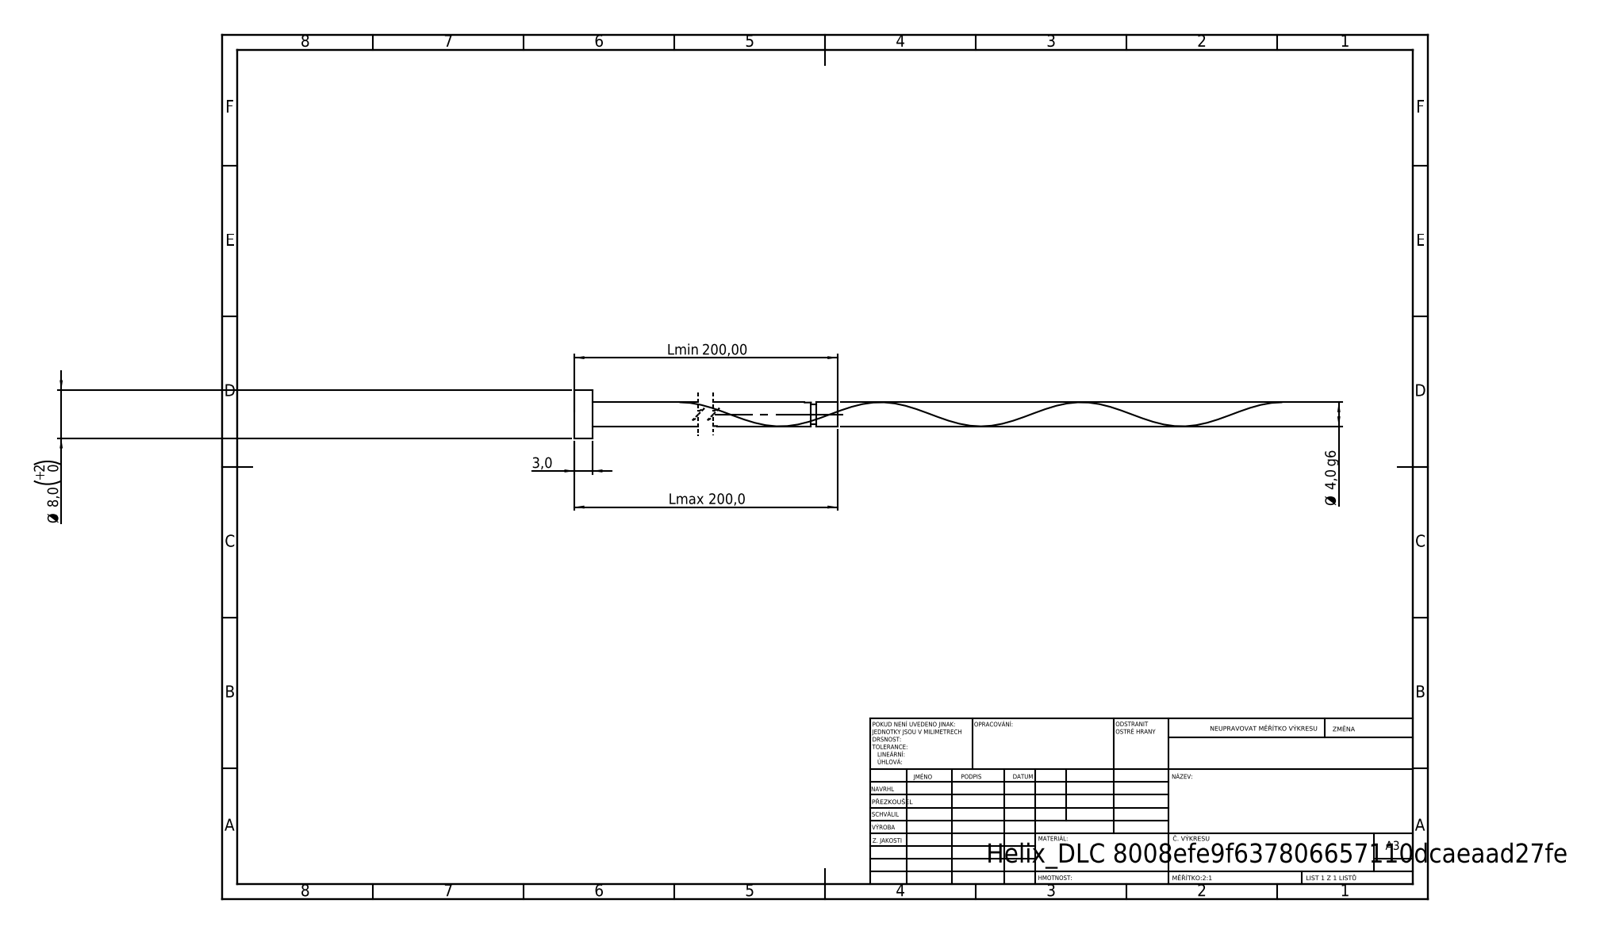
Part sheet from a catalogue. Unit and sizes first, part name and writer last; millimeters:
Units: millimetres
Overall size (bounding box): 200 × 8 × 8
Round bosses / shafts (diameter × count): ⌀8 ×1, ⌀4 ×1, ⌀3.2 ×1
Main face-to-face distances: 3, 200, 197, 196.42, 193.42, 3.58, 195.62, 192.62, 0.8, 4.38
Volume: 2 599 mm³ · Surface area: 2 700 mm²
Bodies: 1 solid, 21 faces (6 planar, 14 cylindrical, 1 other)
STEP written by: SolidWorks 2019 (CONFIG_CONTROL_DESIGN)
